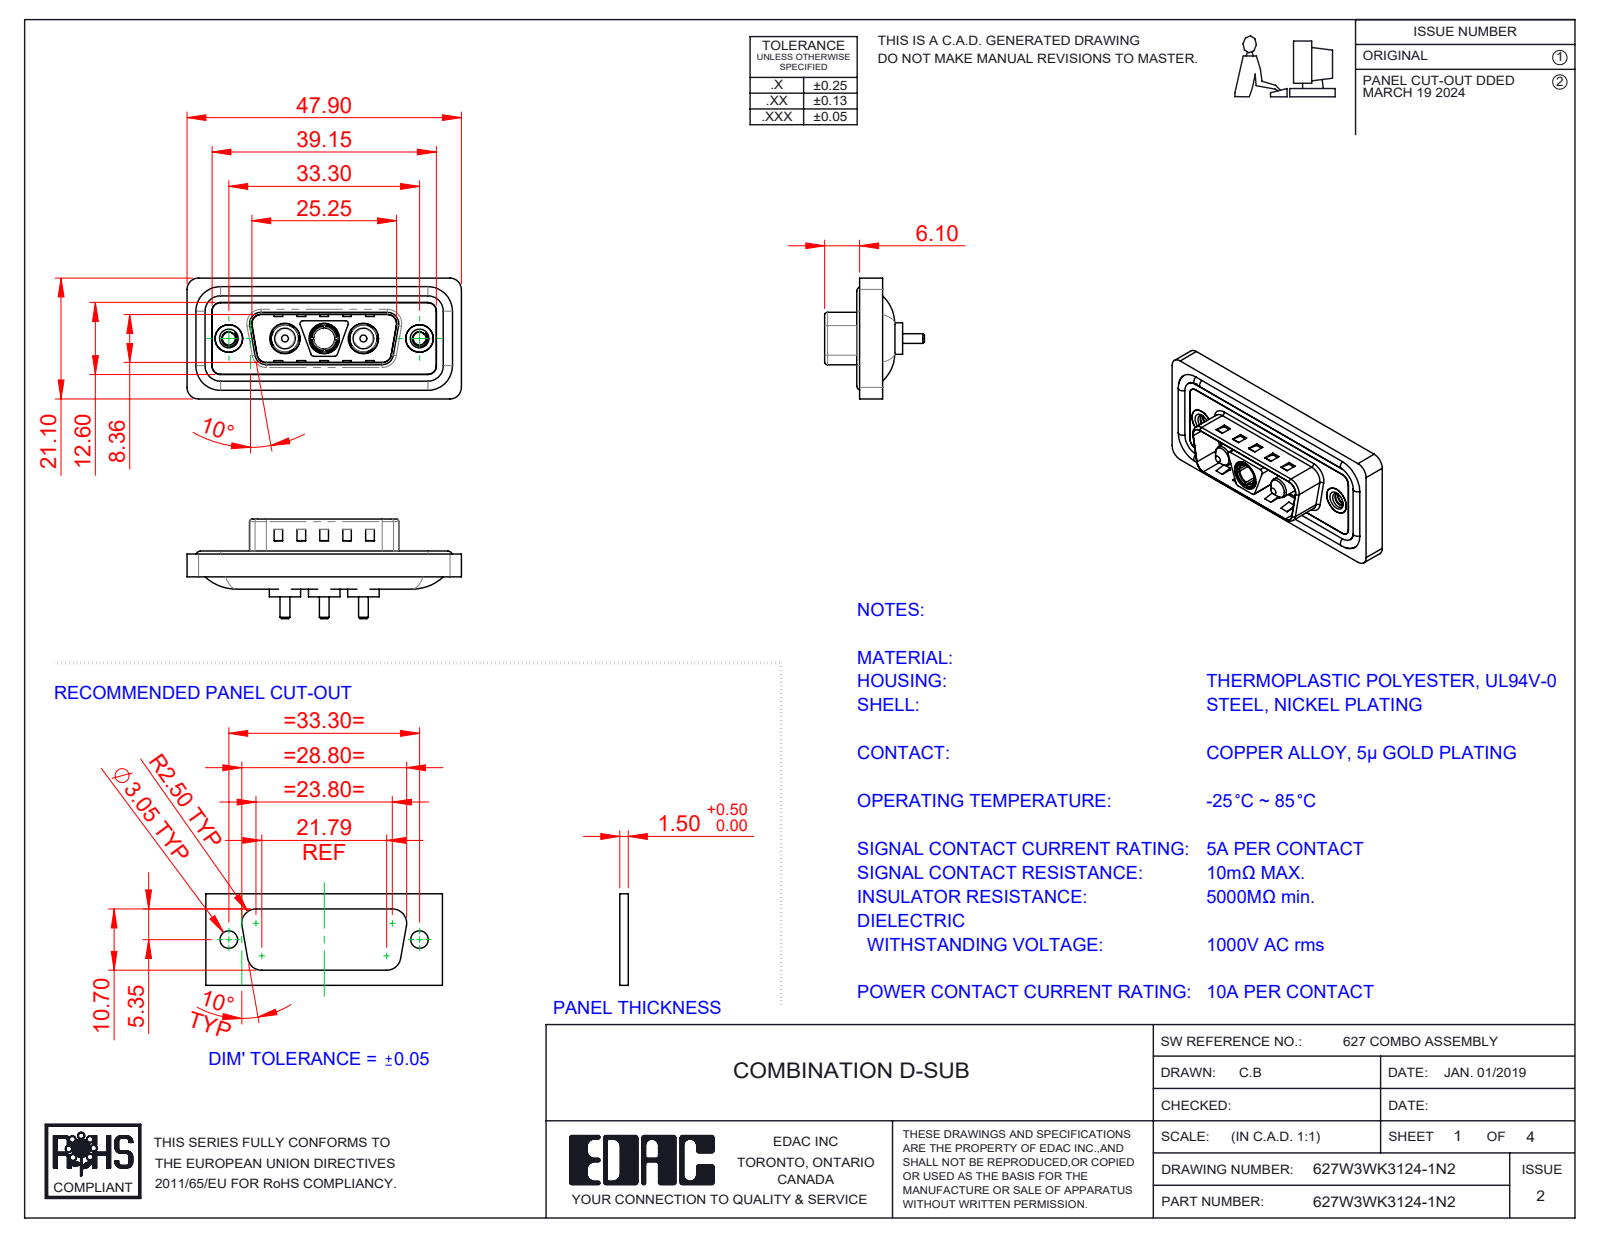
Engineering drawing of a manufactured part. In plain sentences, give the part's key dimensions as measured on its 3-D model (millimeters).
The part is named "627Combo Shell Rear_15 Contacts; 627Combo Housing_3WK3; 627W3WK3124-1N2; Power Pin_10A S (+4 more)". Its 3-D file was written by "SolidWorks 2023 (CONFIG_CONTROL_DESIGN)". It is 13 solids with 609 faces: 231 planar, 250 cylindrical and 128 other. Overall it measures 47.9 by 21.1 by 17.4 millimeters. Its volume is 5 644 cubic millimeters and its surface area 9 089 square millimeters. Round holes: 3 of diameter 4.85, 3 of diameter 5.3, 2 of diameter 2.26, 2 of diameter 4, 2 of diameter 4.8, 2 of diameter 5, 1 of diameter 3.7. Round bosses or shafts: 4 of diameter 1.6, 3 of diameter 5.5, 3 of diameter 5.2, 3 of diameter 4.75, 3 of diameter 3.75, 3 of diameter 1.7, 2 of diameter 4.9, 2 of diameter 3.6. Partial cylindrical surfaces (rounded edges, fillets, slot ends): 26 of radius 1.5, 20 of radius 2, 12 of radius 0.5, 8 of radius 1.6, 4 of radius 0.25, 4 of radius 0.6, 4 of radius 0.65, 4 of radius 0.9. The main face-to-face distances are 0.4, 1.5, 1.1, 0.5, 1.6, 3.1, 2.9, 4, 0.82, 9.58. The hole center spacings are 6.85, 9.8, 16.65, 23.5, 13.7, 33.3.
